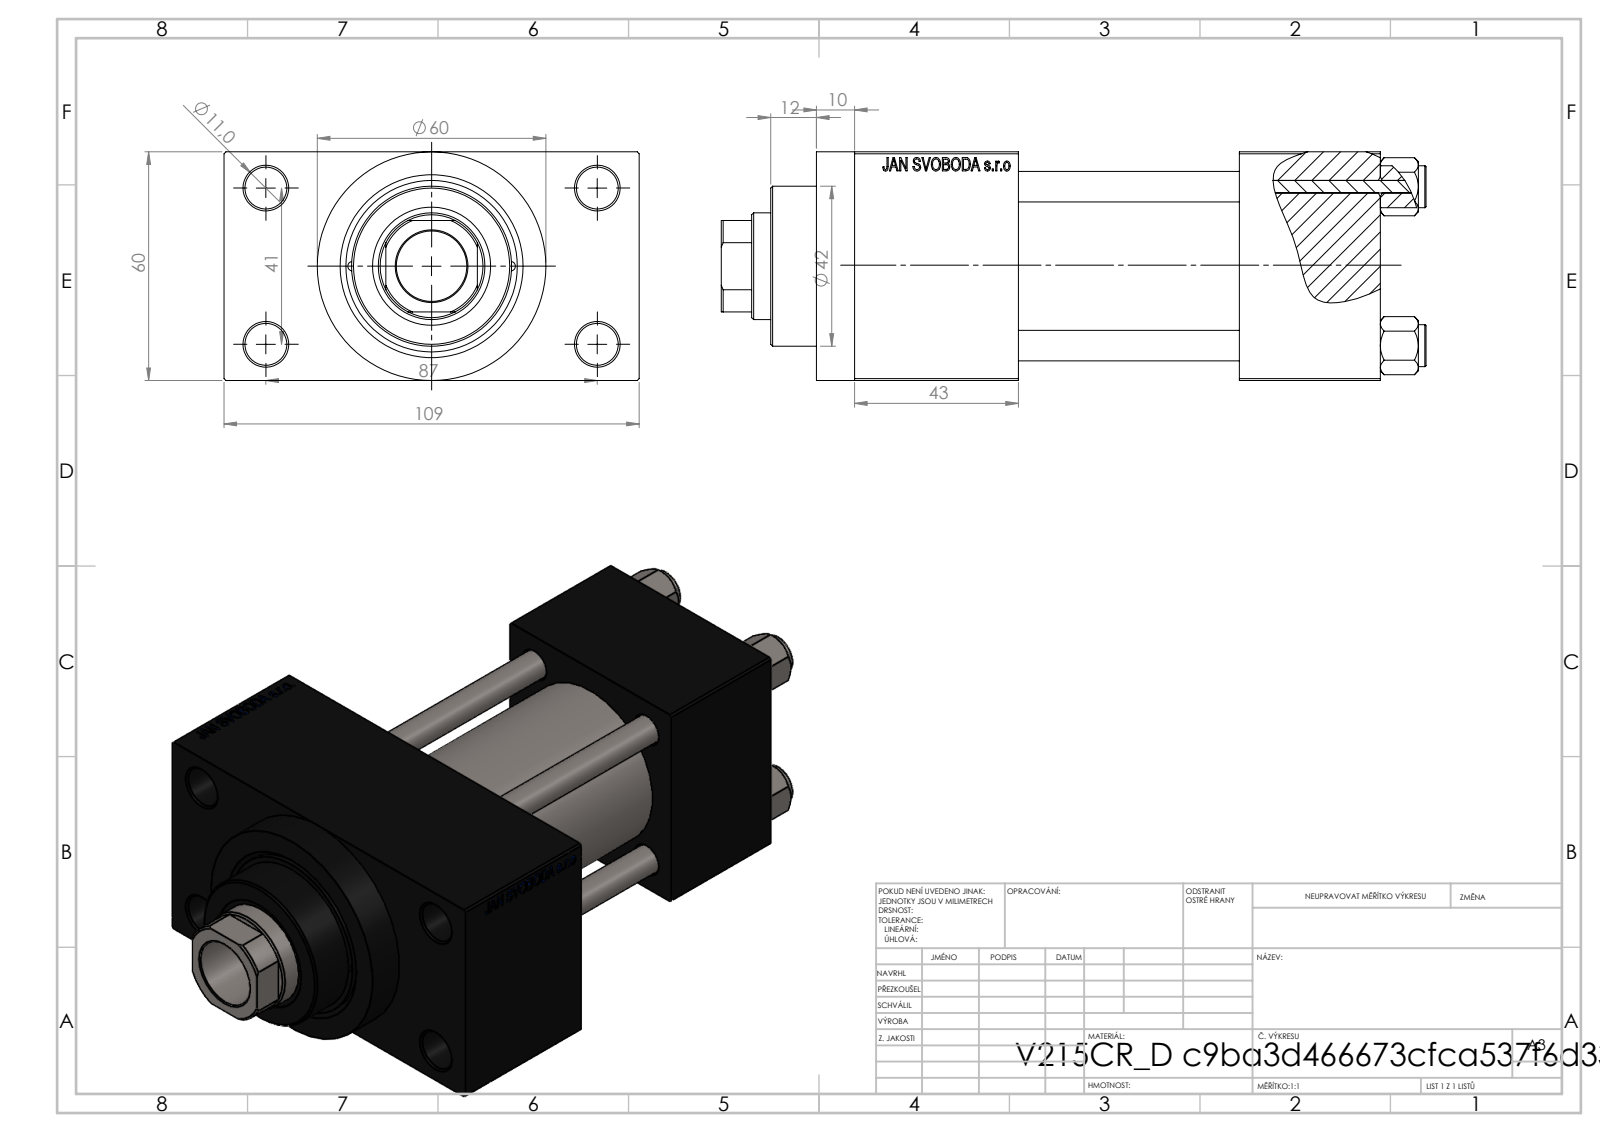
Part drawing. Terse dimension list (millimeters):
name: V215CR_VCP_D; V215_VC_A; V215CR_D_Body; NUT_M5_D (+1 more)
written by: SolidWorks 2019 (CONFIG_CONTROL_DESIGN)
unit: mm
bodies: 11 solids, 1114 faces (502 planar, 92 cylindrical, 520 other)
size: 185 × 109 × 60
volume: 528 665 mm³; area: 129 076 mm²
holes: 4× ⌀8, 4× ⌀11, 2× ⌀2.5, 2× ⌀7, 2× ⌀16.66, 2× ⌀24, 1× ⌀18.5, 1× ⌀28, 1× ⌀31, 1× ⌀40, 1× ⌀45
bosses: 4× ⌀11, 1× ⌀60, 1× ⌀46, 1× ⌀42
rounds: 1× R13.5
face distances: 60, 58, 24.5, 84.5, 37, 95, 138, 101, 43, 109
hole spacings: 20.85, 22.65, 29.49, 30.62, 41.7, 46.53, 47.15, 48.09
